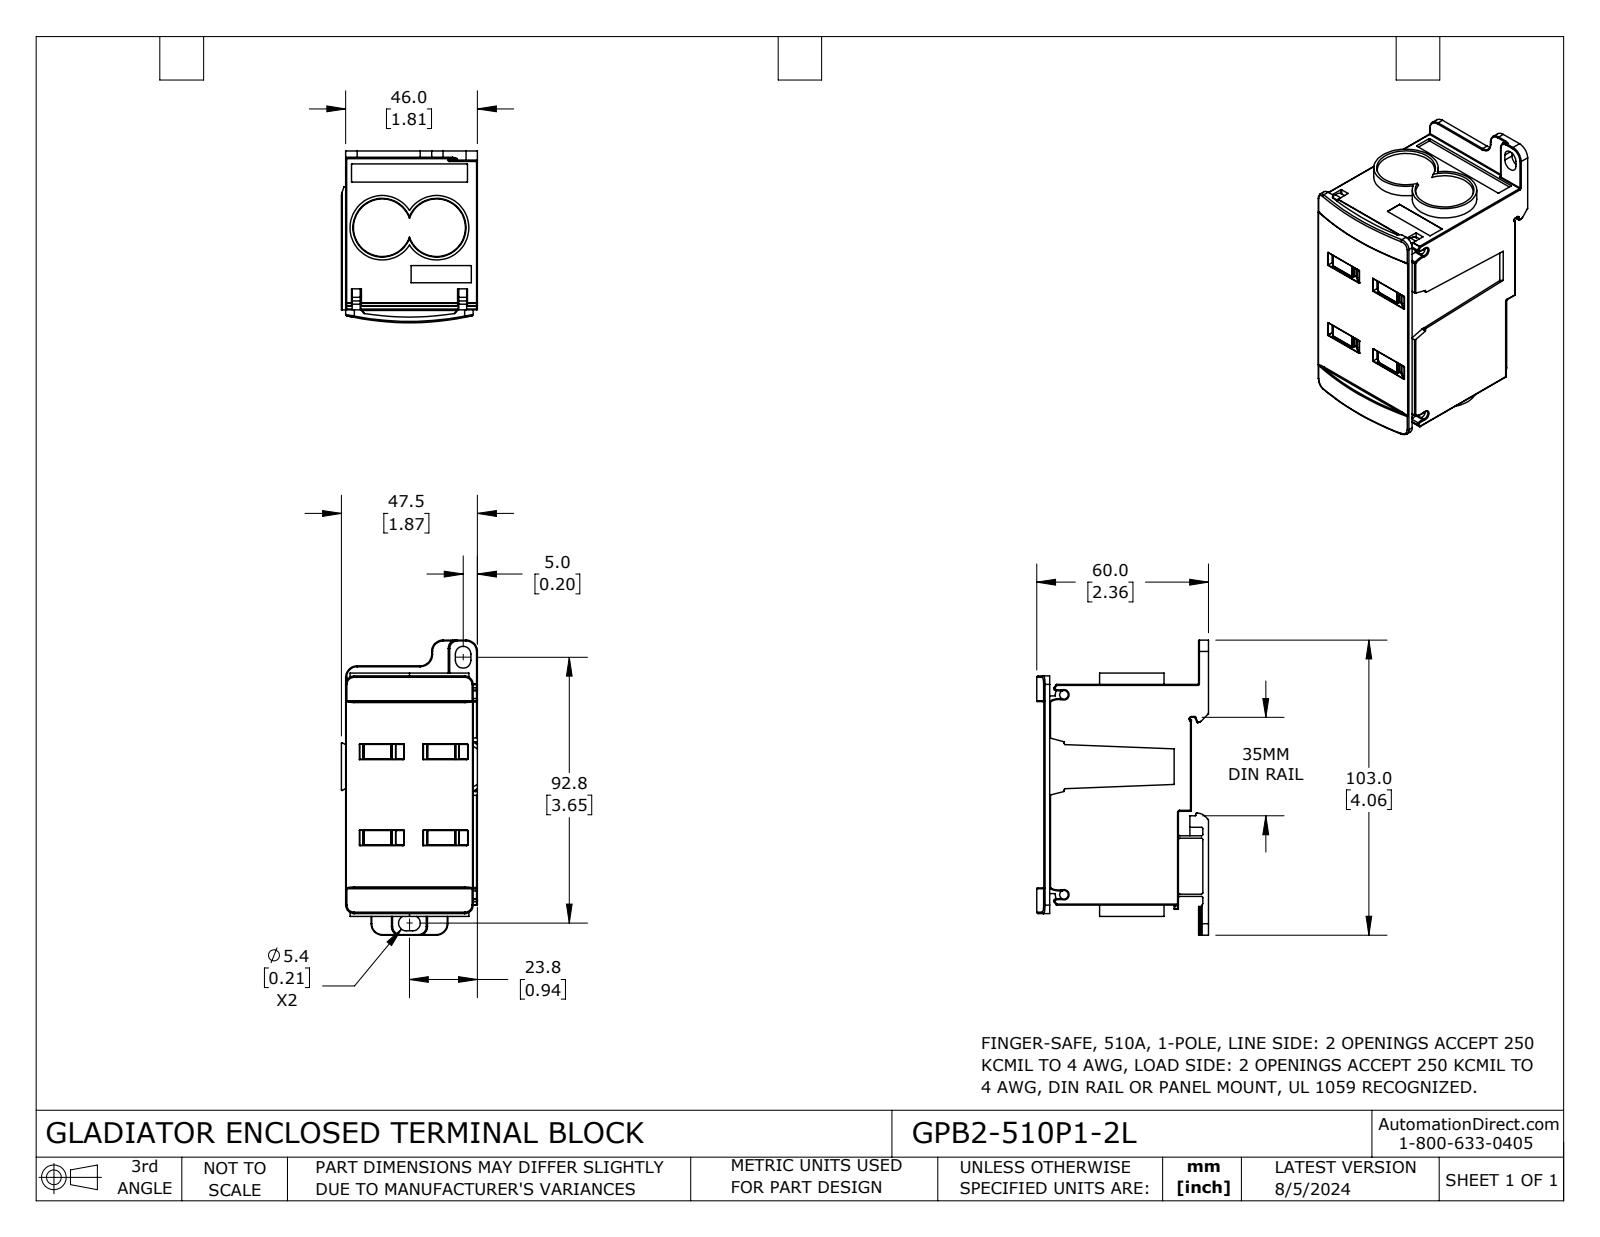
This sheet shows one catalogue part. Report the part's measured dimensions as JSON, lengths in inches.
{"part_name": "GPB2-510P1-2L", "step_written_by": "SolidWorks 2023 (CONFIG_CONTROL_DESIGN)", "units": "inches", "bodies": {"solids": 1, "faces": 743, "planar": 224, "cylindrical": 335, "other": 184}, "overall_size": [4.055, 2.362, 1.87], "volume_in3": 11.59, "surface_area_in2": 43.67, "round_holes": [[0.118, 2]], "round_bosses_or_shafts": [[0.886, 2]], "partial_cylinders_radius": [[0.004, 69], [0.008, 54], [0.012, 45], [0.02, 20], [0.118, 9], [0.157, 7], [0.106, 4], [0.276, 4]], "face_to_face_distances": [1.811, 0.236, 0.118, 2.264, 3.15, 3.031, 2.028, 0.039, 0.079, 0.157], "hole_center_spacings": [2.748]}
